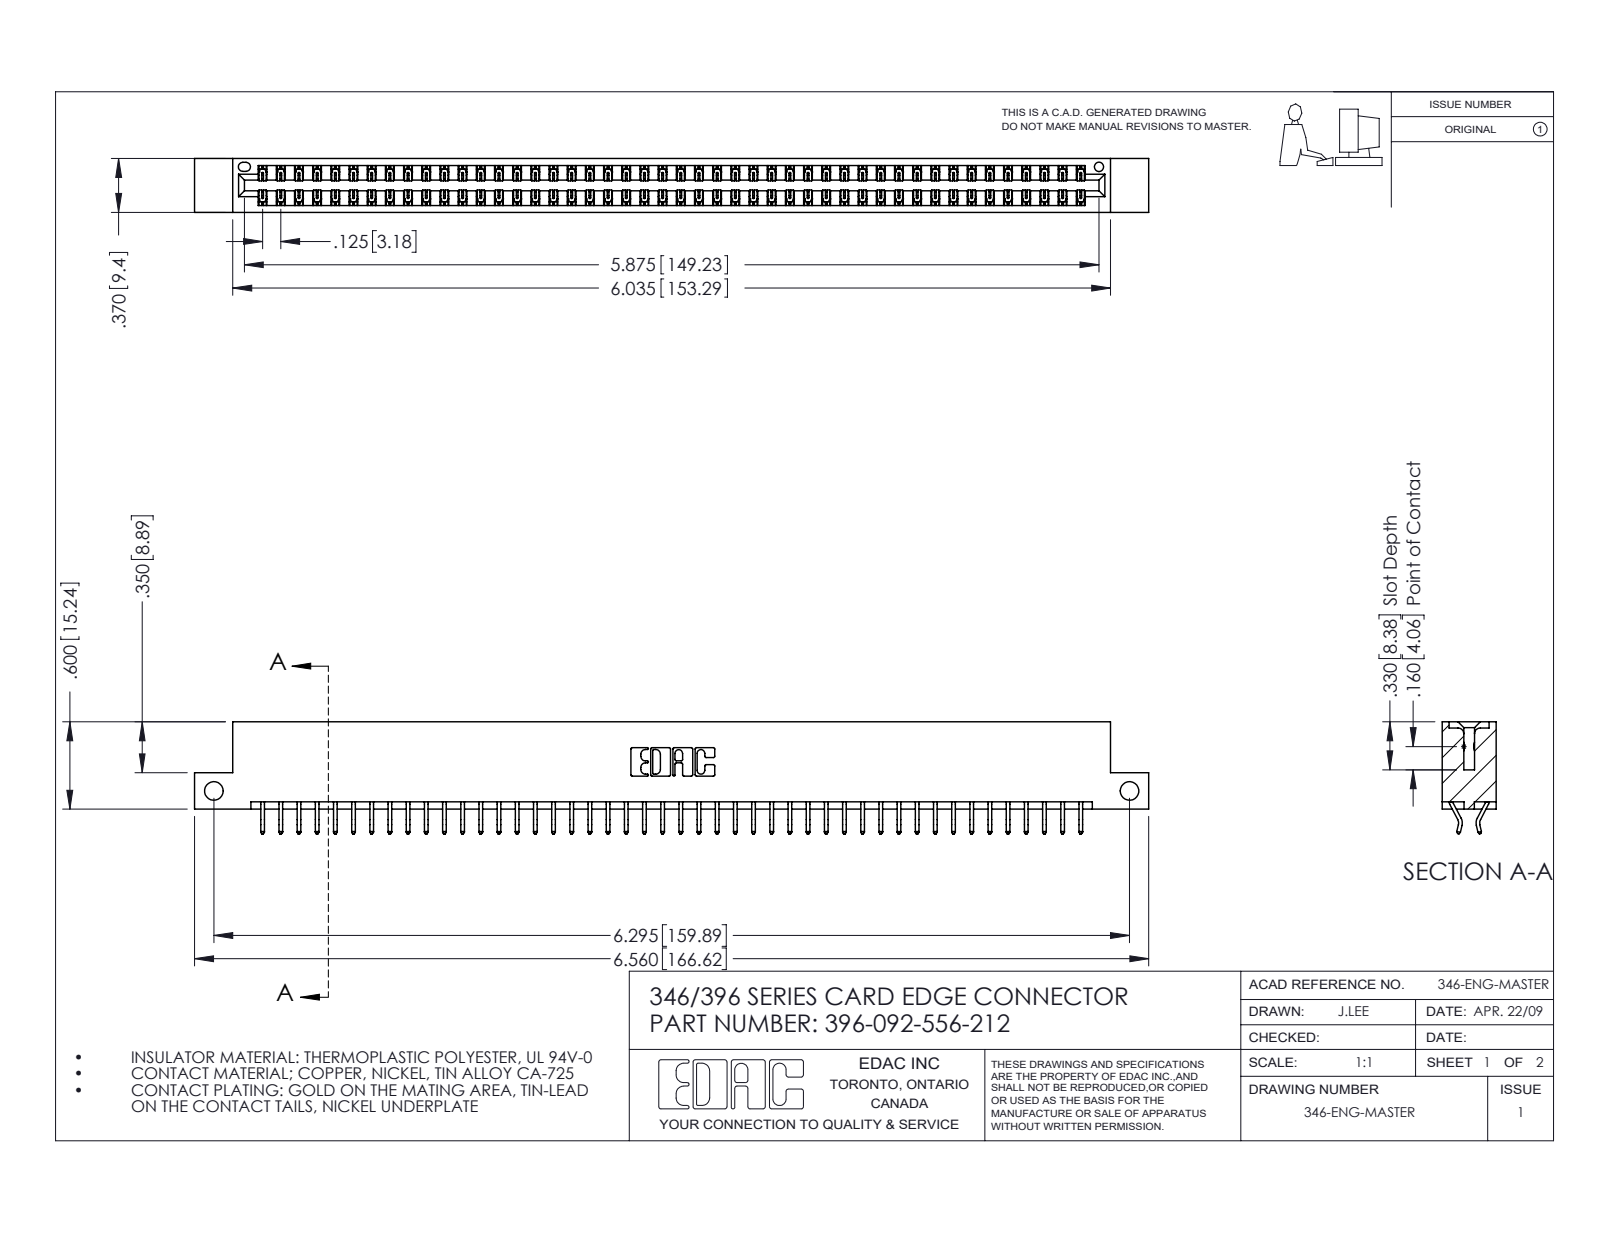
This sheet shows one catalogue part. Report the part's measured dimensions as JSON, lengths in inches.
{"part_name": "396-092-556-212; 346 Part_Flush Mounting Lugs - Side Mount; 345-292-001_556 Tail", "step_written_by": "SolidWorks 2016 (CONFIG_CONTROL_DESIGN)", "units": "inches", "bodies": {"solids": 93, "faces": 5458, "planar": 3664, "cylindrical": 1794, "other": 0}, "overall_size": [6.56, 0.77, 0.37], "volume_in3": 0.988, "surface_area_in2": 34.24, "round_holes": [[0.128, 2], [0.064, 1]], "partial_cylinders_radius": [[0.006, 138], [0.01, 22], [0.007, 6], [0.031, 6], [0.026, 3], [0.01, 2], [0.014, 2], [0.022, 2]], "face_to_face_distances": [0.048, 0.322, 0.37, 0.25, 0.025, 0.072, 0.298, 0.275, 0.148, 0.222], "hole_center_spacings": [6.295]}
